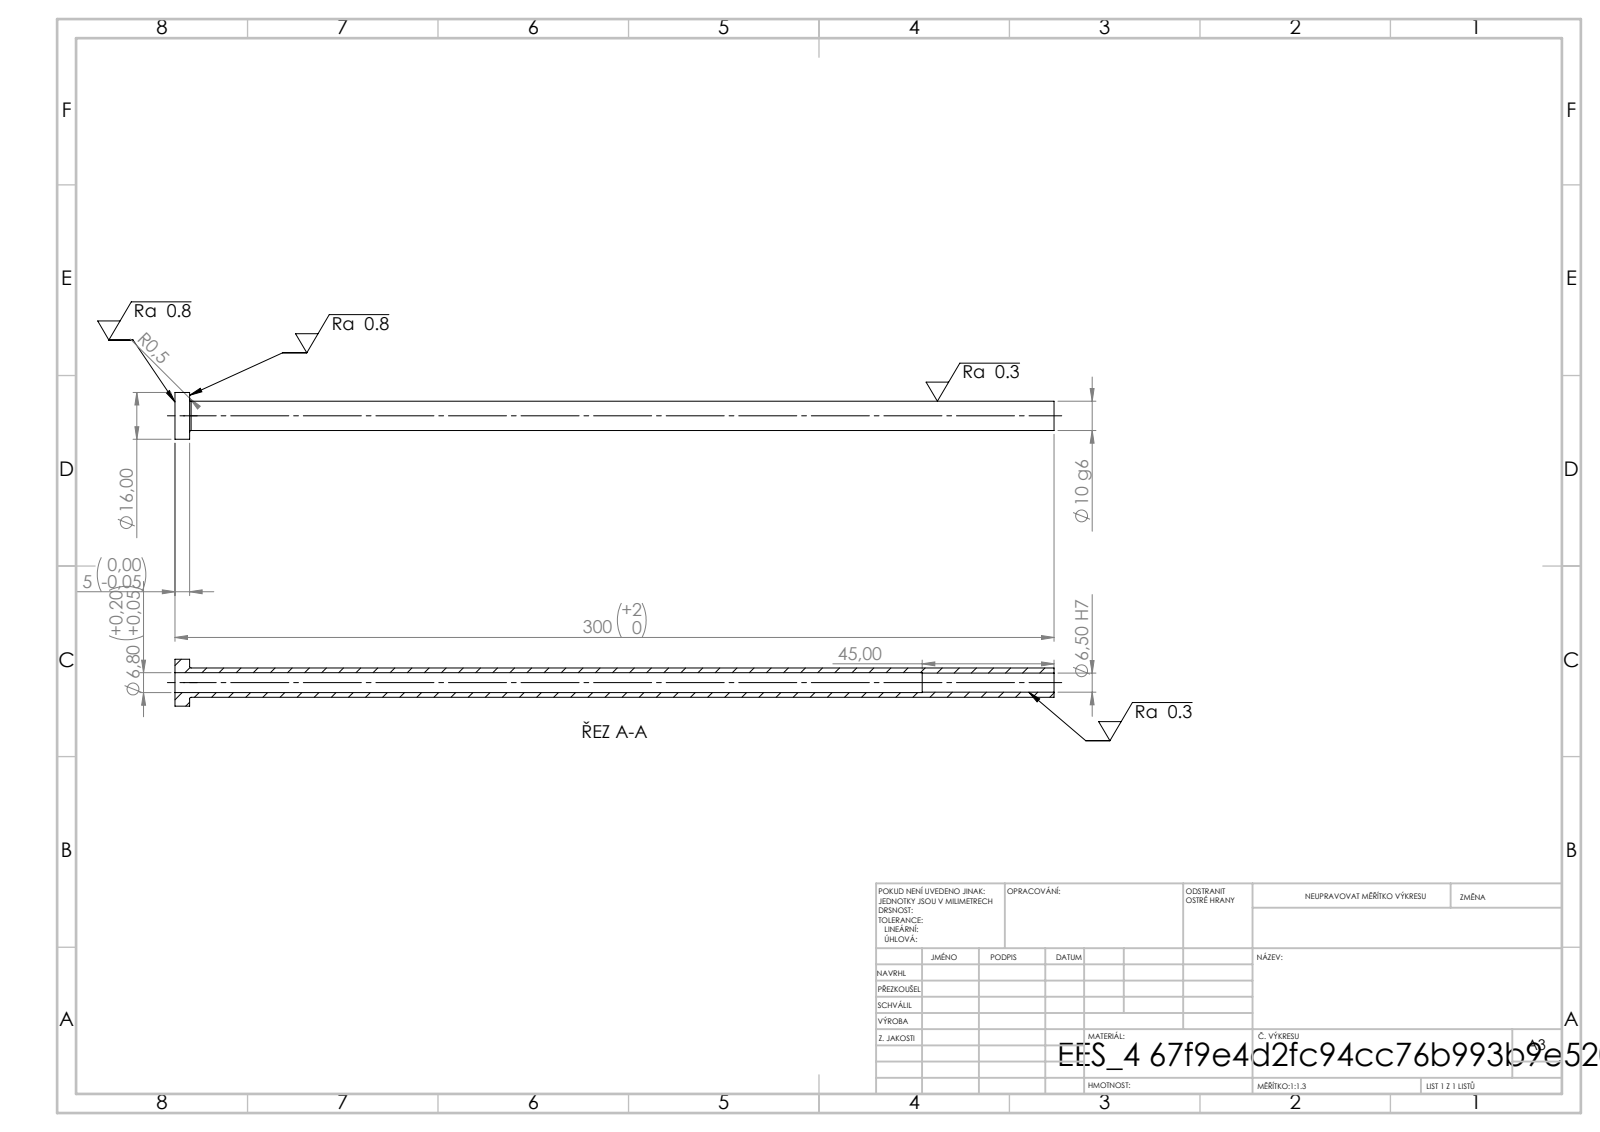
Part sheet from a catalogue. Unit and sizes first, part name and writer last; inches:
Units: inches
Overall size (bounding box): 11.811 × 0.63 × 0.63
Round holes (diameter × count): ⌀0.256 ×1, ⌀0.268 ×1
Round bosses / shafts (diameter × count): ⌀0.63 ×1, ⌀0.394 ×1
Main face-to-face distances: 0.197, 11.811, 11.614, 10.039, 9.843, 1.772
Volume: 0.819 in³ · Surface area: 25.13 in²
Bodies: 1 solid, 14 faces (4 planar, 8 cylindrical, 2 other)
STEP written by: SolidWorks 2019 (CONFIG_CONTROL_DESIGN)
